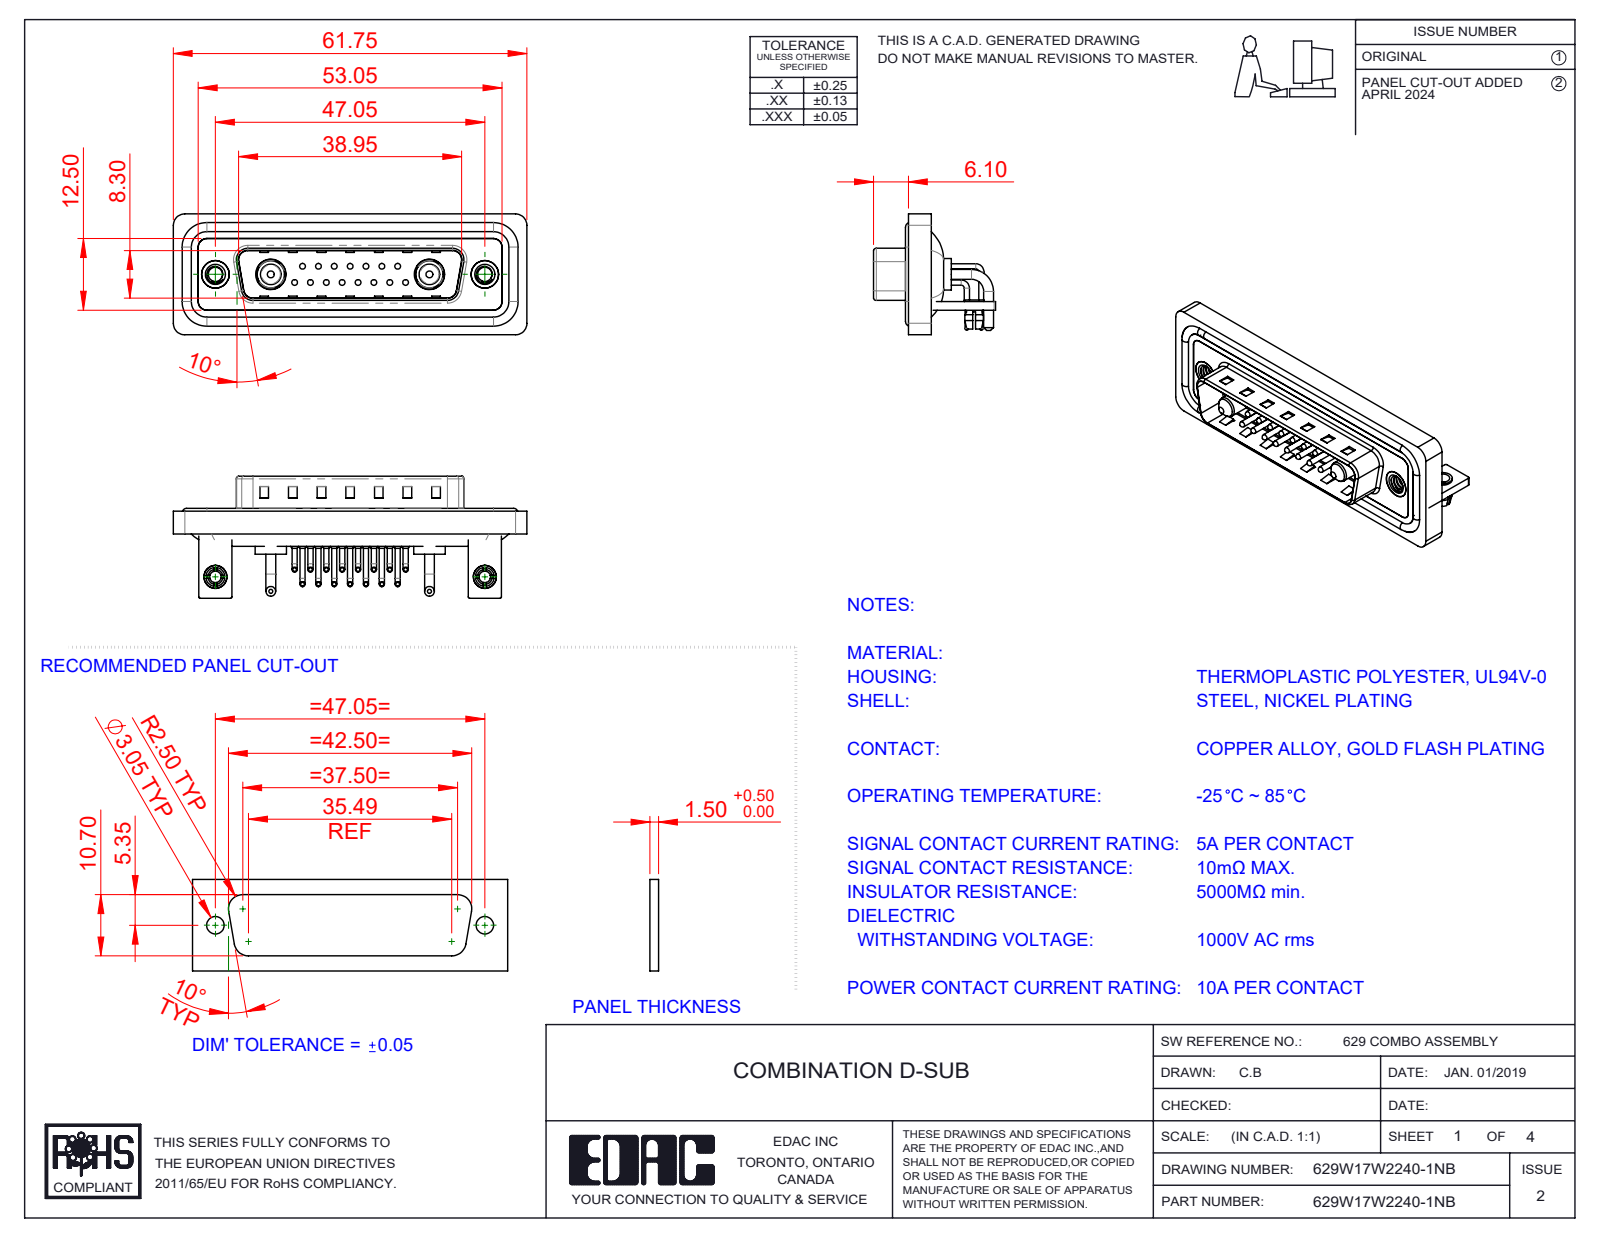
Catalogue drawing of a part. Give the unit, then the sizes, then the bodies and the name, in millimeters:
Units: millimetres
Overall size (bounding box): 61.75 × 21.3 × 21.1
Round holes (diameter × count): ⌀2 ×17, ⌀0.75 ×15, ⌀1.6 ×15, ⌀2.5 ×4, ⌀3.2 ×2, ⌀4 ×2, ⌀4.8 ×2, ⌀4.85 ×2, ⌀5 ×2, ⌀5.3 ×2
Round bosses / shafts (diameter × count): ⌀0.9 ×30, ⌀1.5 ×15, ⌀1 ×15, ⌀0.65 ×15, ⌀1.7 ×4, ⌀1.6 ×4, ⌀5.5 ×2, ⌀5.2 ×2
Partial cylindrical surfaces — rounded edges, fillets, slot ends (radius × count): R2 ×19, R1.5 ×18, R0.25 ×16, R1.01 ×15, R0.5 ×9, R1.6 ×8, R0.6 ×4, R0.65 ×4
Main face-to-face distances: 0.4, 0.8, 1.5, 2.1, 2.9, 1.1, 4.1, 1.6, 4.5, 3.7
Hole centre spacings: 3.16, 2.77, 5.54, 8.31, 5.04, 7.49, 11.08, 5.03
Volume: 7 704 mm³ · Surface area: 13 298 mm²
Bodies: 30 solids, 2349 faces (1257 planar, 820 cylindrical, 272 other)
Part name (STEP PRODUCT): 629Combo Board Lock; 629Combo Contact Row 2; 629Combo Shell Front_25 Contacts; 629W17W2140-1NB (+7 more)
STEP written by: SolidWorks 2023 (CONFIG_CONTROL_DESIGN)
